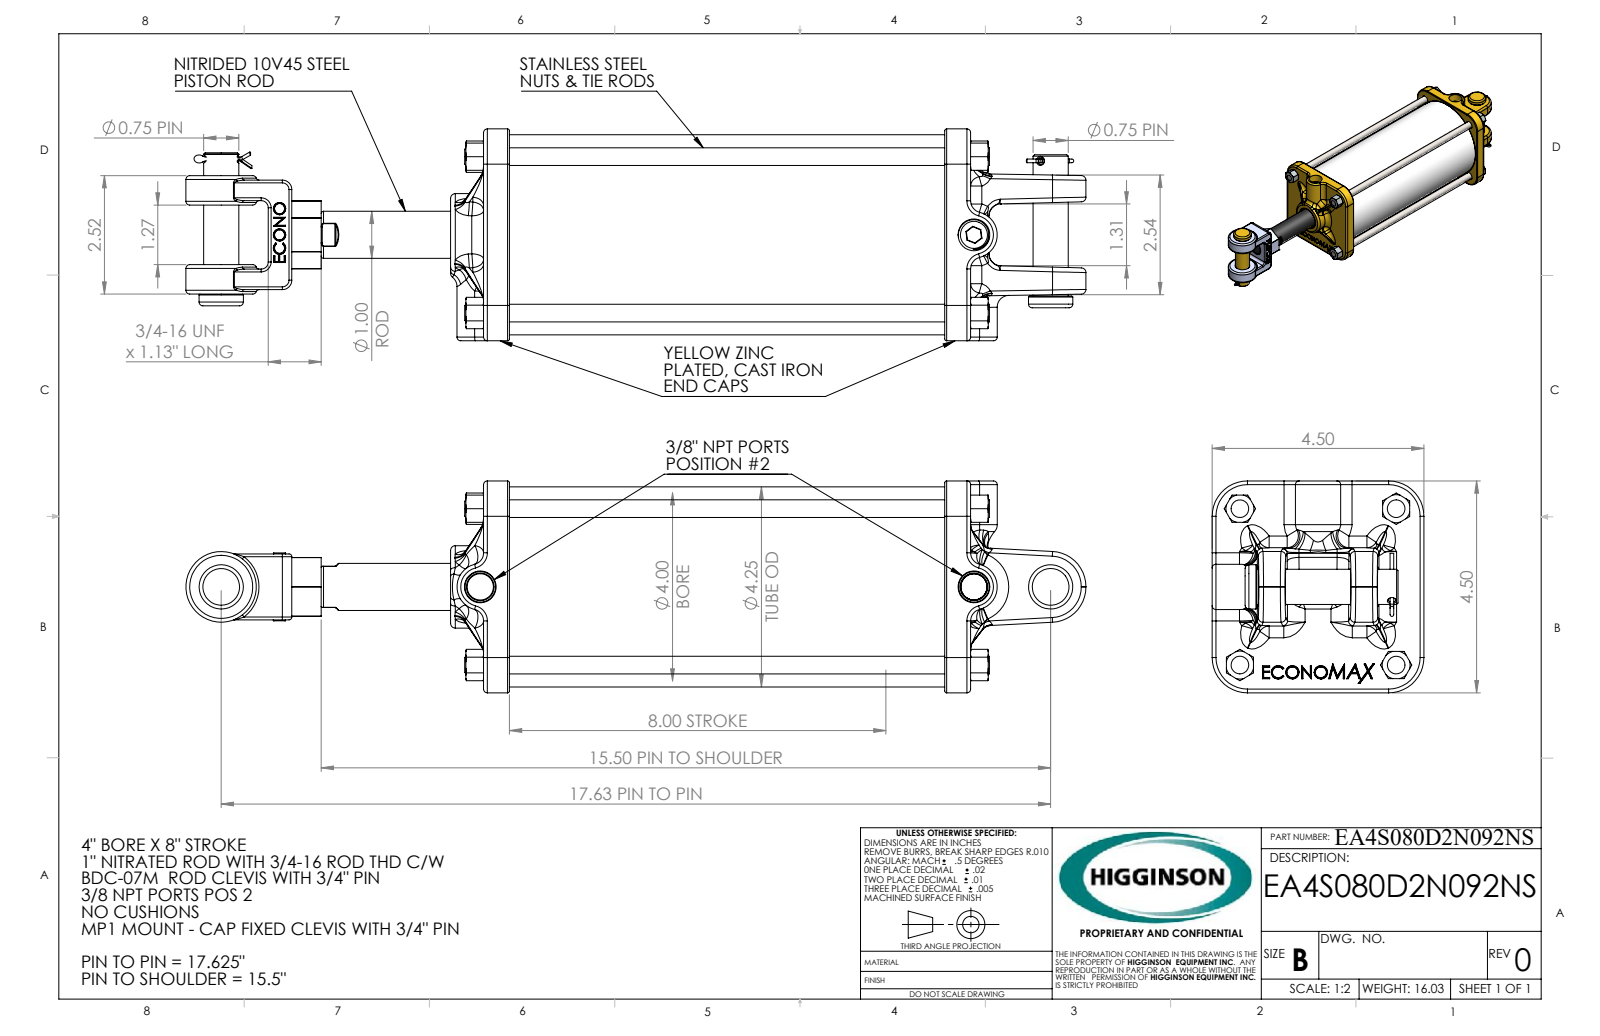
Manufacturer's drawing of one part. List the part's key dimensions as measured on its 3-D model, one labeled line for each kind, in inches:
Part name (STEP PRODUCT): 18cotter pin X .75; APT40-0.75-16; BDC-07M; 5409-06V (+8 more)
STEP written by: SolidWorks 2021 (CONFIG_CONTROL_DESIGN)
Units: inches
Bodies: 23 solids, 1677 faces (416 planar, 252 cylindrical, 1009 other)
Overall size (bounding box): 19.125 × 4.5 × 4.5
Volume: 78.1 in³ · Surface area: 599.8 in²
Round holes (diameter × count): ⌀0.16 ×2, ⌀0.562 ×2, ⌀0.687 ×1, ⌀0.75 ×1, ⌀0.751 ×1, ⌀0.754 ×1, ⌀0.785 ×1, ⌀1.05 ×1, ⌀1.128 ×1, ⌀1.14 ×1, ⌀1.142 ×1, ⌀1.371 ×1
Round bosses / shafts (diameter × count): ⌀0.375 ×4, ⌀0.94 ×2, ⌀0.747 ×2, ⌀4.25 ×1, ⌀3.992 ×1, ⌀3.985 ×1, ⌀3.74 ×1, ⌀3.634 ×1
Partial cylindrical surfaces — rounded edges, fillets, slot ends (radius × count): R0.25 ×19, R0.06 ×14, R0.1 ×12, R0.04 ×8, R0.08 ×8, R0.039 ×7, R0.75 ×7, R0.01 ×6
Main face-to-face distances: 0.55, 9.8, 9.25, 1.25, 10.35, 1.8, 8, 8.55, 1.24, 4.5
Hole centre spacings: 1.613, 1.63, 15.995, 17.625
